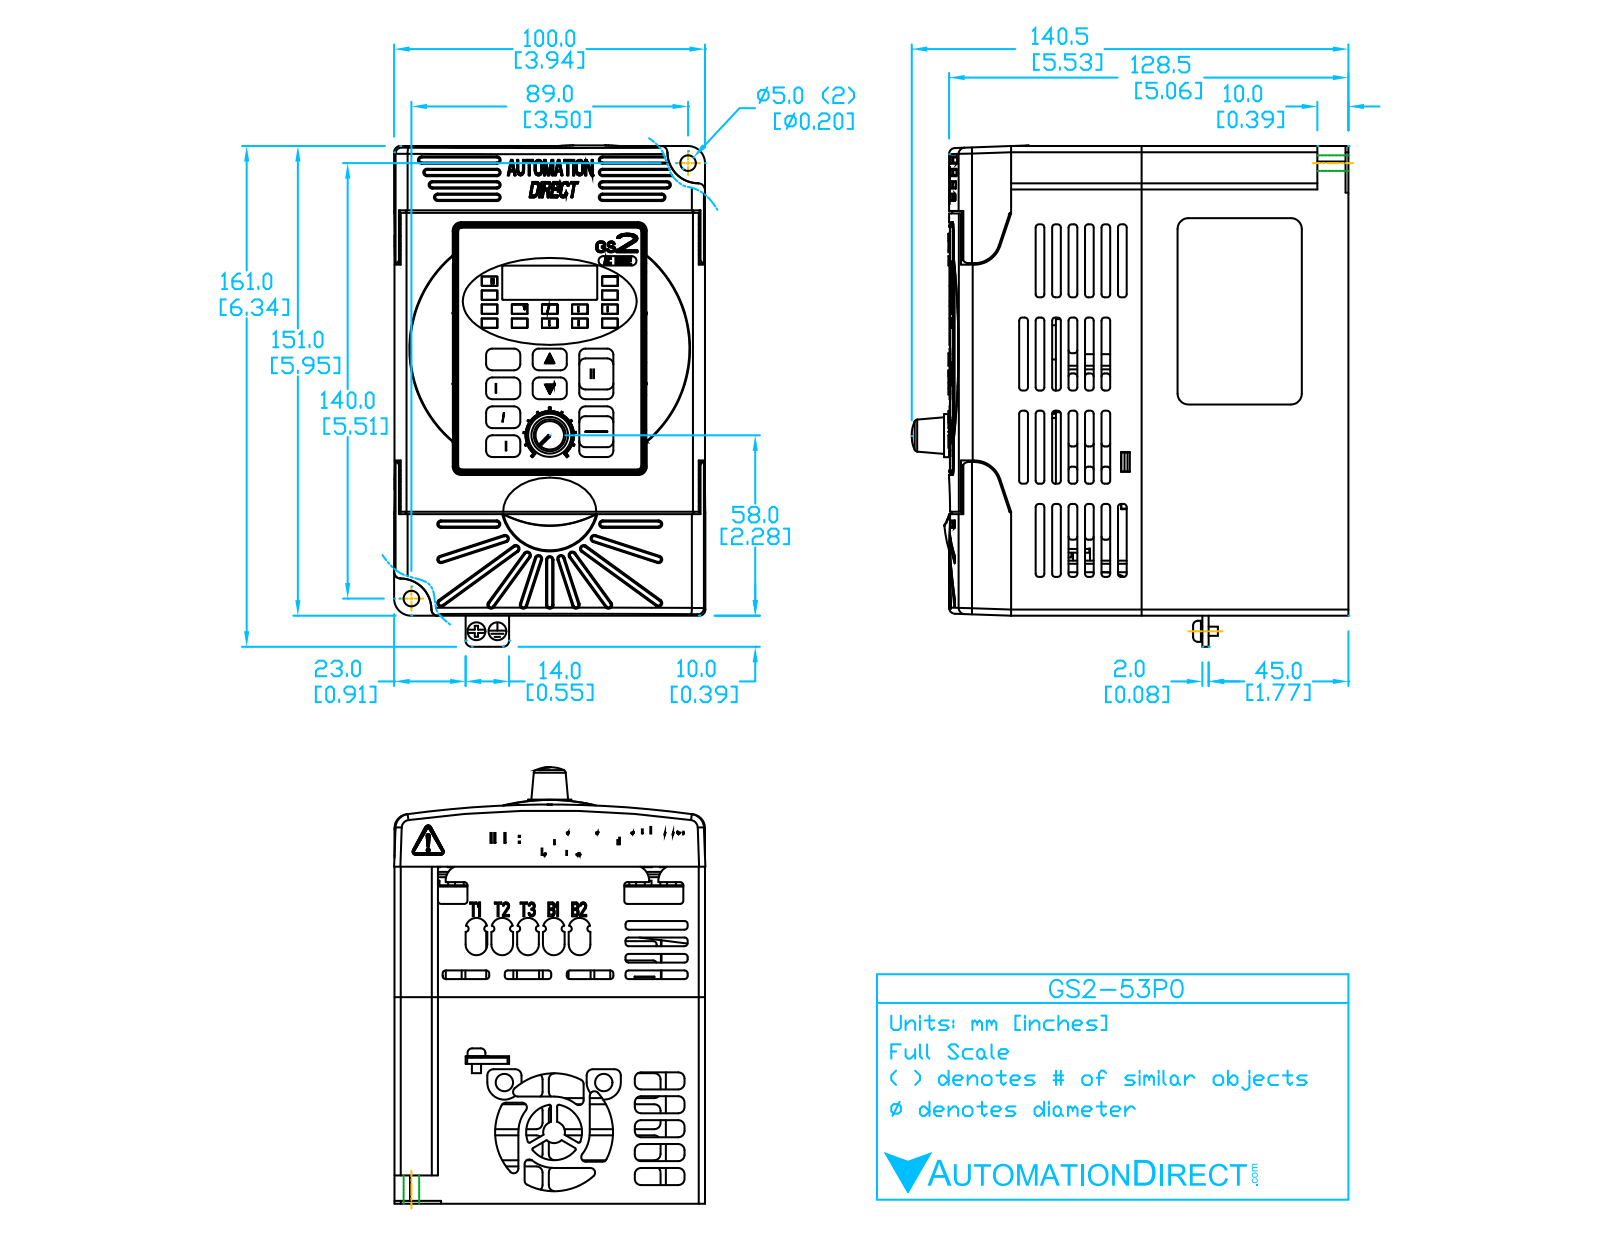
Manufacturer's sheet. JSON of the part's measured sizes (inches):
{"part_name": "GS2-53P0", "step_written_by": "SolidWorks 2013 (AUTOMOTIVE_DESIGN)", "units": "inches", "bodies": {"solids": 1, "faces": 753, "planar": 329, "cylindrical": 220, "other": 204}, "overall_size": [6.345, 5.495, 3.94], "volume_in3": 112.9, "surface_area_in2": 196.7, "round_holes": [[0.2, 2], [0.7, 1], [1.46, 1]], "round_bosses_or_shafts": [[0.545, 1], [0.22, 1], [0.15, 1]], "partial_cylinders_radius": [[0.04, 40], [0.06, 16], [0.03, 14], [0.125, 10], [0.03, 8], [0.045, 6], [0.2, 6], [0.1, 4]], "face_to_face_distances": [3.94, 5.95, 4.256, 4.266, 0.015, 5.935, 0.03, 0.761, 3.179, 0.03], "hole_center_spacings": [6.528]}
